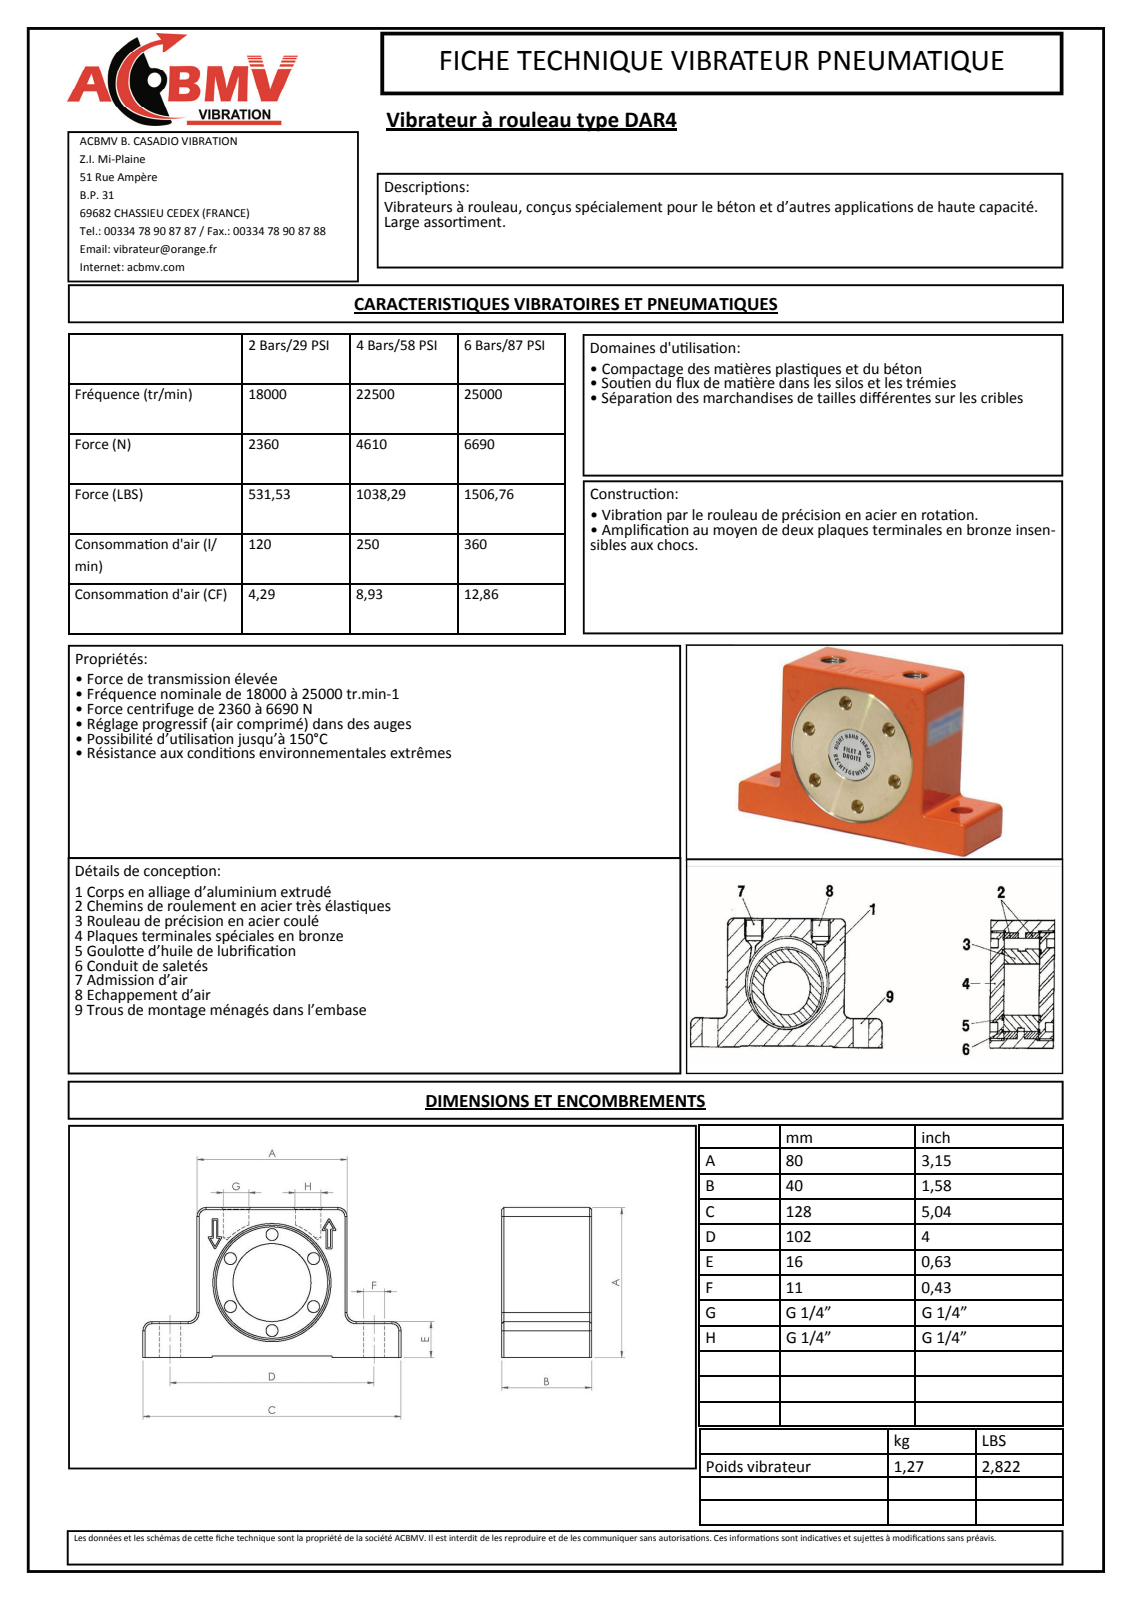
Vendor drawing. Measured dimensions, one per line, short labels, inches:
name: 7004-00-M
written by: Autodesk Inventor 2011 (CONFIG_CONTROL_DESIGN)
unit: in
bodies: 1 solid, 337 faces (205 planar, 91 cylindrical, 41 other)
size: 5.039 × 3.15 × 1.575
volume: 16.87 in³; area: 52.39 in²
holes: 6× ⌀0.236, 2× ⌀0.433, 2× ⌀0.451, 1× ⌀0.117, 1× ⌀1.024
bosses: 1× ⌀0.106
rounds: 29× R0.012, 6× R0.118, 4× R0.03, 3× R0.035, 3× R0.041, 3× R0.077, 3× R0.081, 3× R0.1
face distances: 1.575, 3.15, 0.02, 3.13, 2.52, 0.63, 0.61, 1.555, 0.945, 4.094
hole spacings: 1.024, 1.773, 1.142, 1.773, 2.048, 2.953, 0.548, 1.29
